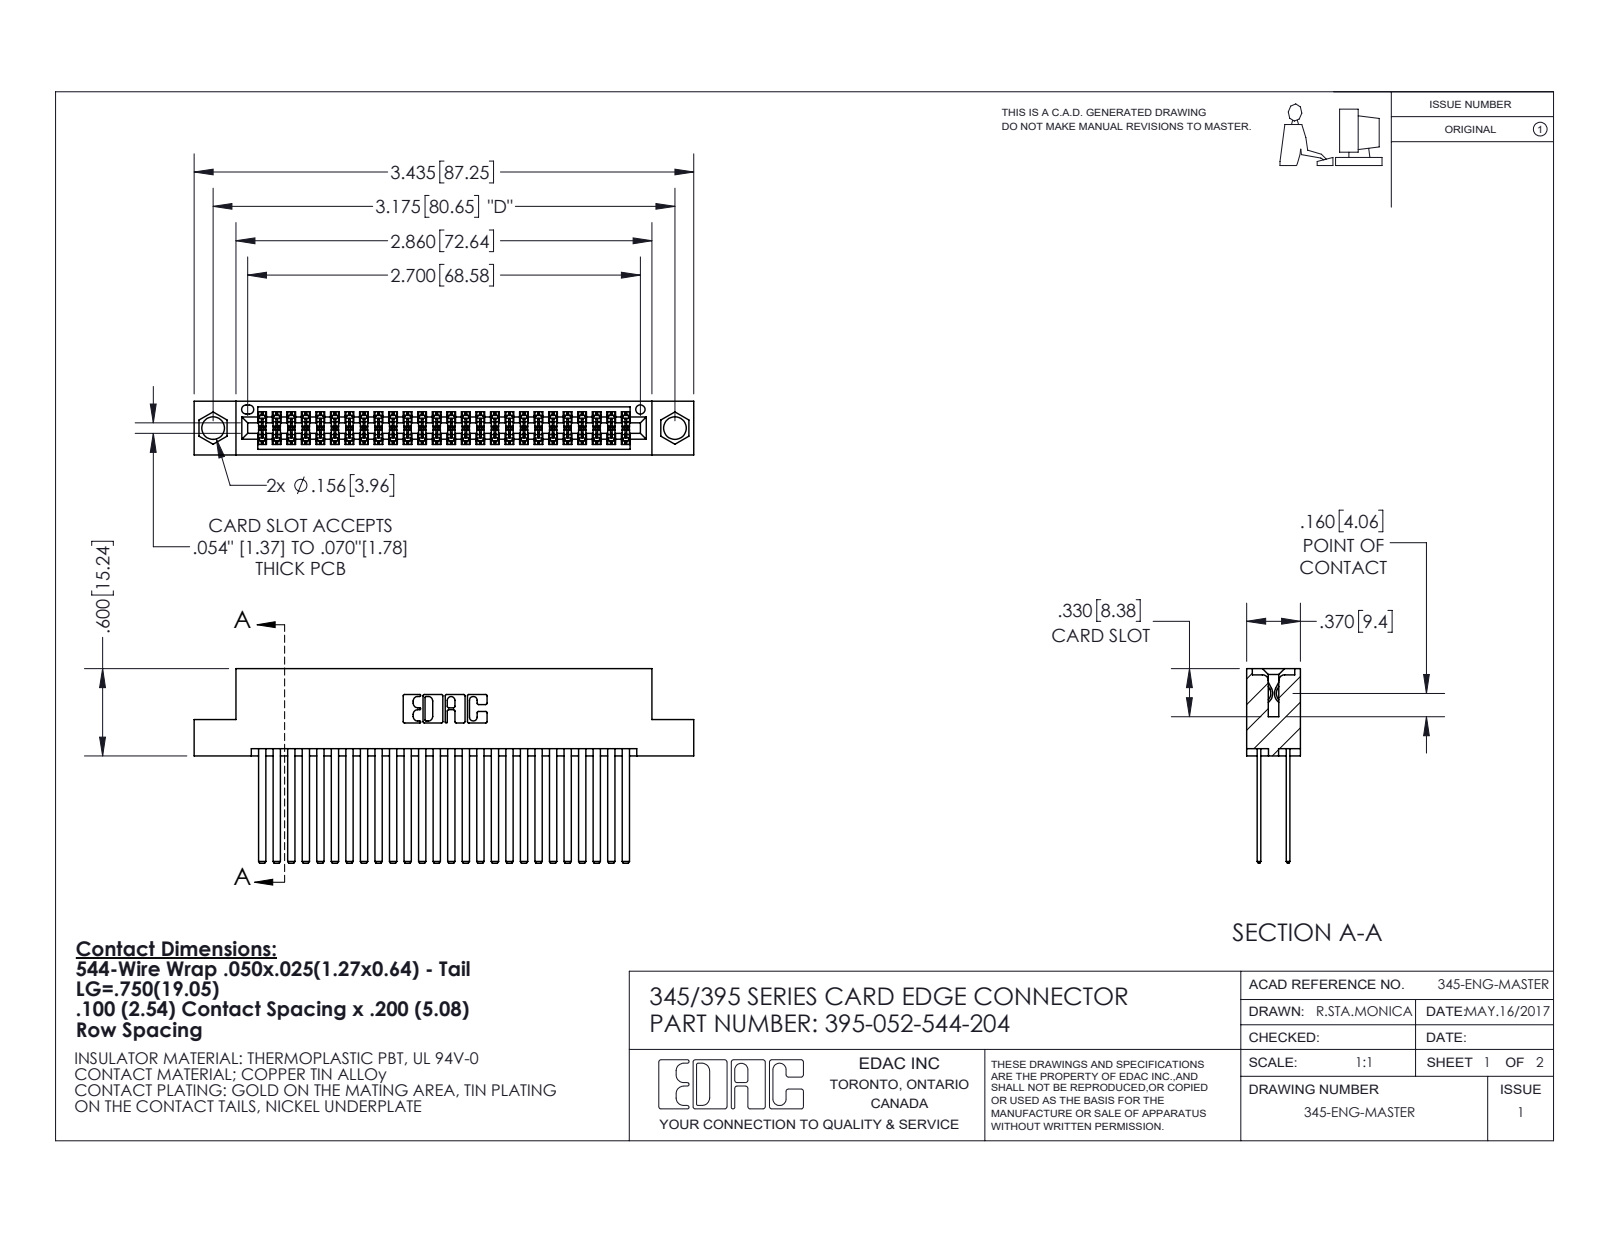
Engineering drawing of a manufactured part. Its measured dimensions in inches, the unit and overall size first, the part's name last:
Units: inches
Overall size (bounding box): 3.435 × 1.337 × 0.37
Round holes (diameter × count): ⌀0.156 ×2, ⌀0.064 ×1
Partial cylindrical surfaces — rounded edges, fillets, slot ends (radius × count): R0.006 ×104, R0.01 ×22, R0.007 ×6, R0.031 ×6, R0.026 ×3, R0.014 ×2, R0.019 ×2, R0.022 ×2
Main face-to-face distances: 0.2, 0.072, 0.298, 0.025, 0.098, 0.272, 0.225, 0.175, 0.37, 0.05
Hole centre spacings: 0.27, 2.94, 3.175
Volume: 0.546 in³ · Surface area: 23.11 in²
Bodies: 53 solids, 2428 faces (1602 planar, 826 cylindrical, 0 other)
Part name (STEP PRODUCT): 345 Part_Flush Mounting Lugs - 0.156 Dia-TI; 395-052-544-204; 345-292-001_345-293-144
STEP written by: SolidWorks 2020 (CONFIG_CONTROL_DESIGN)
